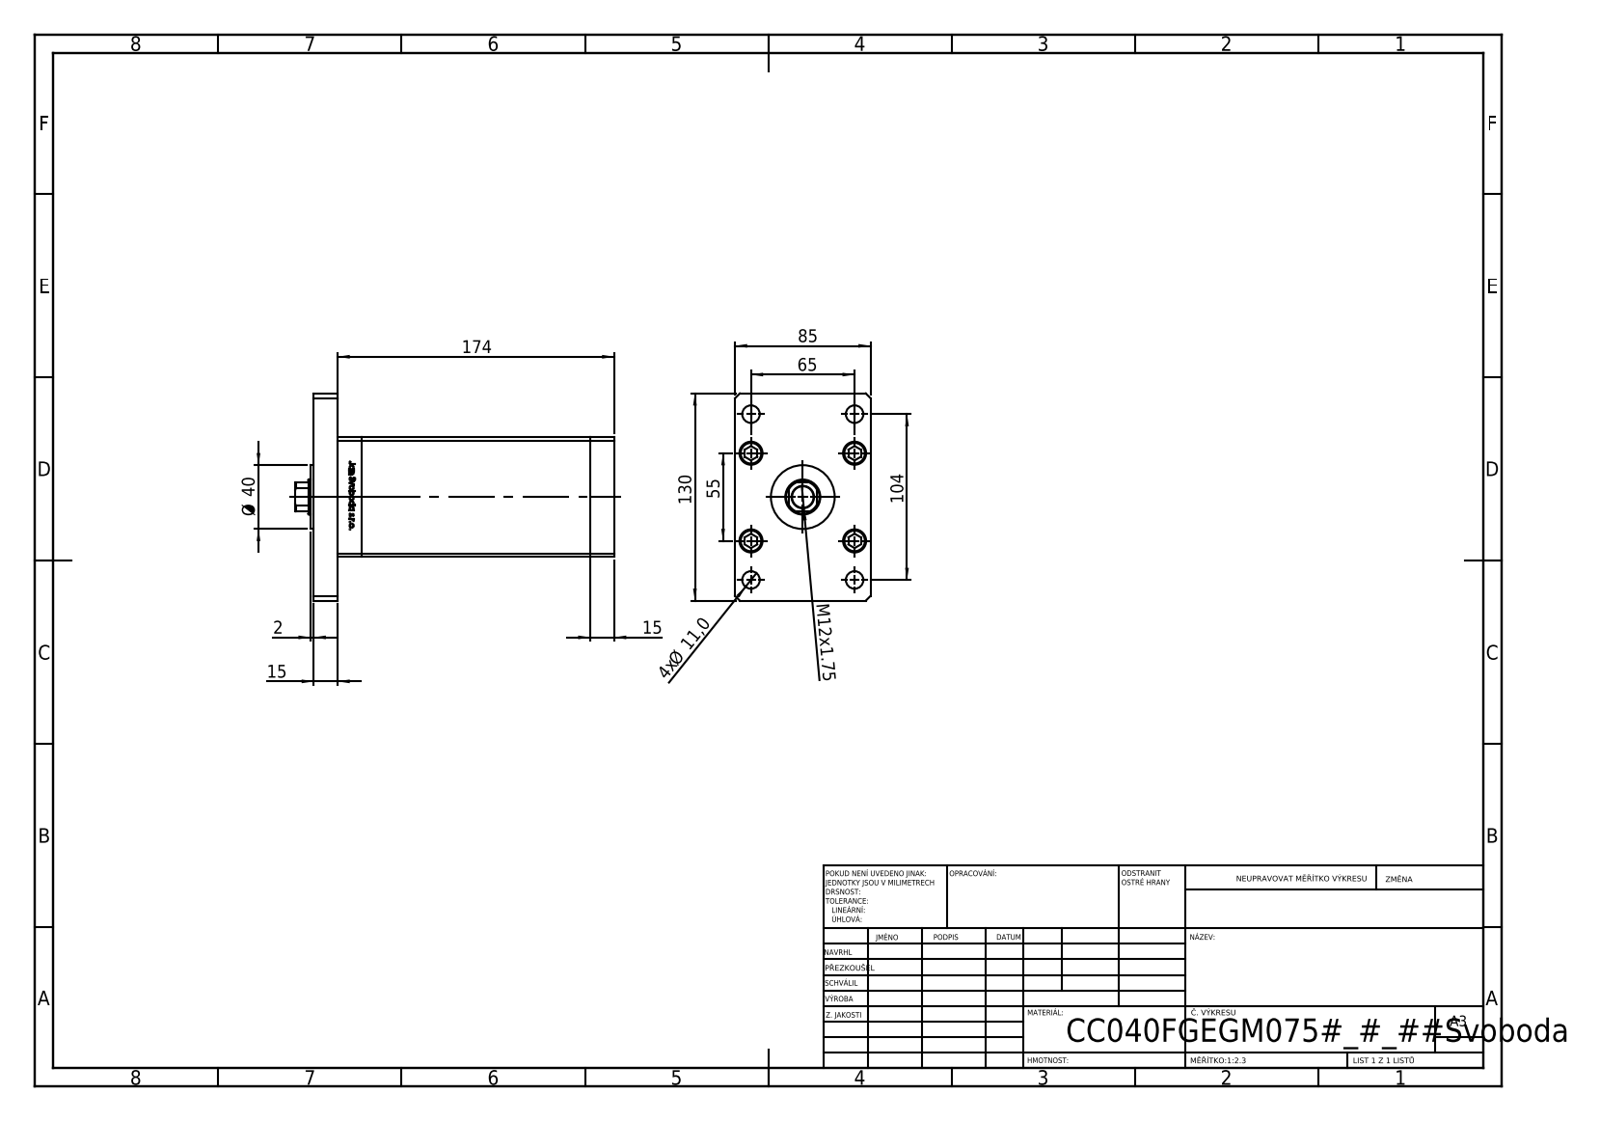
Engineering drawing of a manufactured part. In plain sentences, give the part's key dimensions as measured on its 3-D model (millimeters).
The part is named "V220C BACK_F; V220C_FRONT_F; V220C_F; V220C_VC_F (+2 more)". Its 3-D file was written by "SolidWorks 2019 (CONFIG_CONTROL_DESIGN)". It is 19 solids with 1310 faces: 517 planar, 187 cylindrical and 606 other. Overall it measures 200 by 130 by 85 millimeters. Its volume is 1 139 000 cubic millimeters and its surface area 196 216 square millimeters. Round holes: 9 of diameter 11, 5 of diameter 15.5, 4 of diameter 10, 4 of diameter 14.5, 2 of diameter 2, 2 of diameter 13.16, 1 of diameter 13.5, 1 of diameter 22, 1 of diameter 23.5. Round bosses or shafts: 9 of diameter 8, 5 of diameter 14.5, 1 of diameter 40. Partial cylindrical surfaces (rounded edges, fillets, slot ends): 2 of radius 0.93, 1 of radius 10.5. The main face-to-face distances are 15, 85, 158.5, 173.5, 75, 30, 143.5, 188.5, 10.5, 27.5. The hole center spacings are 28, 24.5, 42.57, 61.32, 65, 69.46, 79.5, 102.69.
